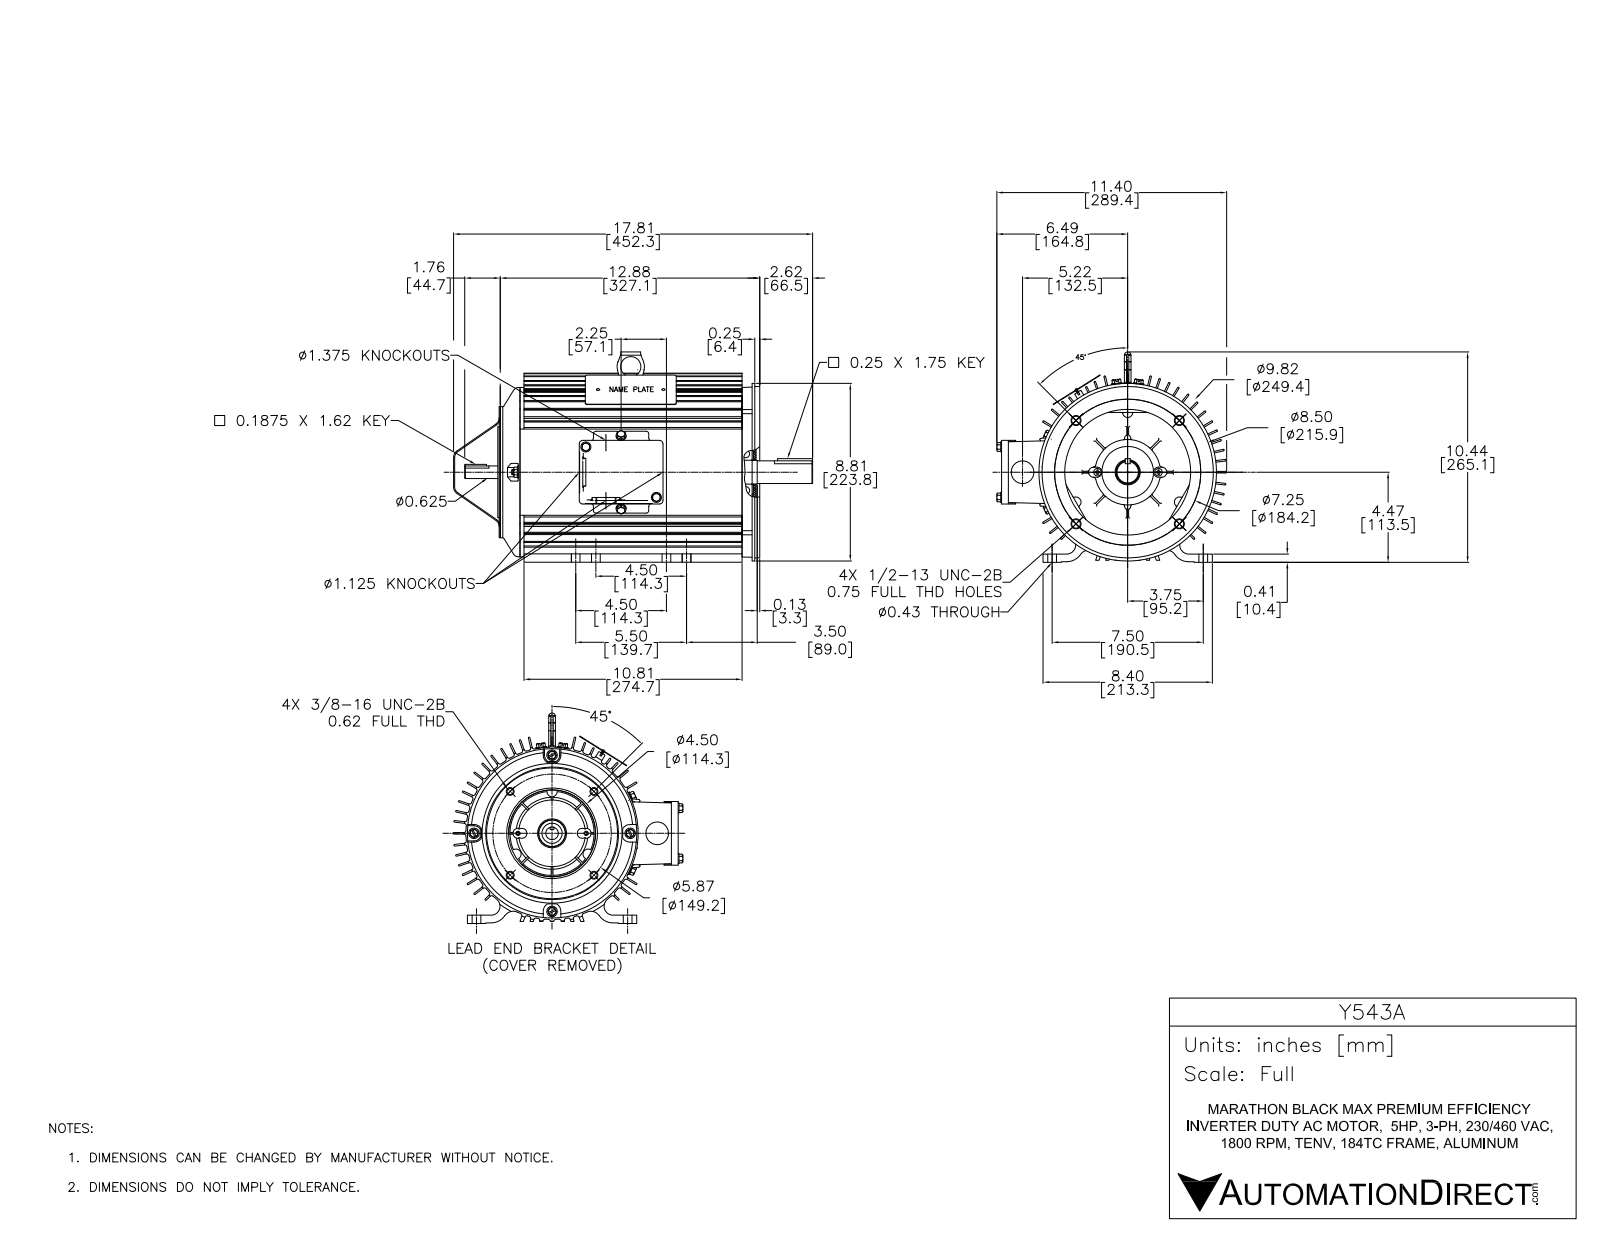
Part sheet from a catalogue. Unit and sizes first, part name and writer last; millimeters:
Units: millimetres
Overall size (bounding box): 449.6 × 297.1 × 264.3
Round holes (diameter × count): ⌀10.9 ×8, ⌀5.7 ×5, ⌀5.1 ×4, ⌀6.8 ×4, ⌀7.1 ×4, ⌀8 ×4, ⌀10.3 ×4, ⌀10.7 ×4, ⌀5.3 ×2, ⌀5.4 ×2, ⌀5.6 ×2, ⌀28.6 ×2
Round bosses / shafts (diameter × count): ⌀13.2 ×10, ⌀6.4 ×10, ⌀12.7 ×4, ⌀9.5 ×4, ⌀9.5 ×2, ⌀7.8 ×2, ⌀4.8 ×2, ⌀223.8 ×1
Partial cylindrical surfaces — rounded edges, fillets, slot ends (radius × count): R0.8 ×118, R1.5 ×102, R2.5 ×78, R1 ×33, R1.3 ×23, R3.3 ×16, R0.6 ×12, R6.4 ×7
Main face-to-face distances: 2, 2, 1.2, 324.1, 22.4, 301.8, 10.4, 3.3, 212.9, 112.5
Hole centre spacings: 73.2, 176, 118.5, 69.8, 107.4, 160.1, 139.2, 17.5
Volume: 2 665 000 mm³ · Surface area: 1 245 000 mm²
Bodies: 31 solids, 4727 faces (928 planar, 1056 cylindrical, 2743 other)
Part name (STEP PRODUCT): 036109ME-1100_Rev02
STEP written by: SolidWorks 2015 (CONFIG_CONTROL_DESIGN)
